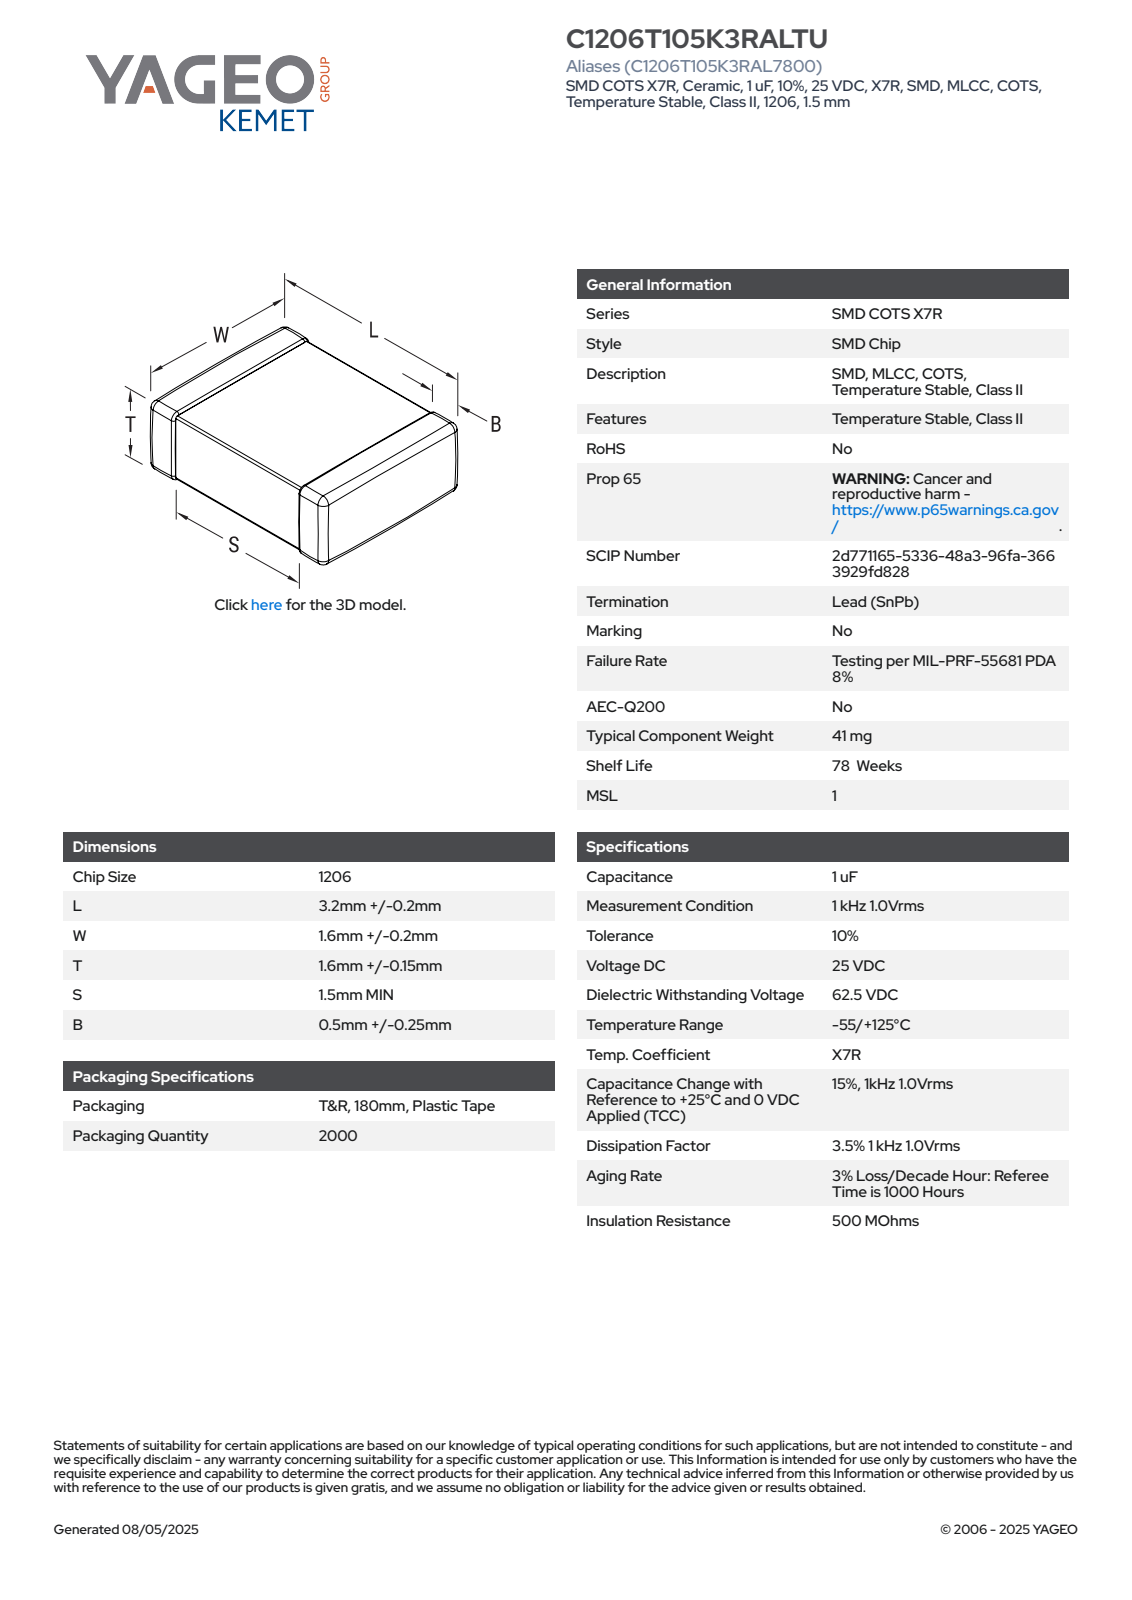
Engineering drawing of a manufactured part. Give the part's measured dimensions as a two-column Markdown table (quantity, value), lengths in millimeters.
| quantity | value |
| --- | --- |
| part name | CCS_STDNOS_1206_L3.4W1.8T1.75B0.5 |
| STEP written by | SolidWorks 2014 (AUTOMOTIVE_DESIGN) |
| units | millimeters |
| bodies | 4 solids, 125 faces (71 planar, 38 cylindrical, 16 other) |
| overall size | 3.4 × 1.8 × 1.75 |
| volume | 10 mm³ |
| surface area | 30 mm² |
| main face-to-face distances | 1.72, 1.67, 1.71, 3.4, 1.76, 1.75, 1.8, 1.68, 0.72, 0.68 |
